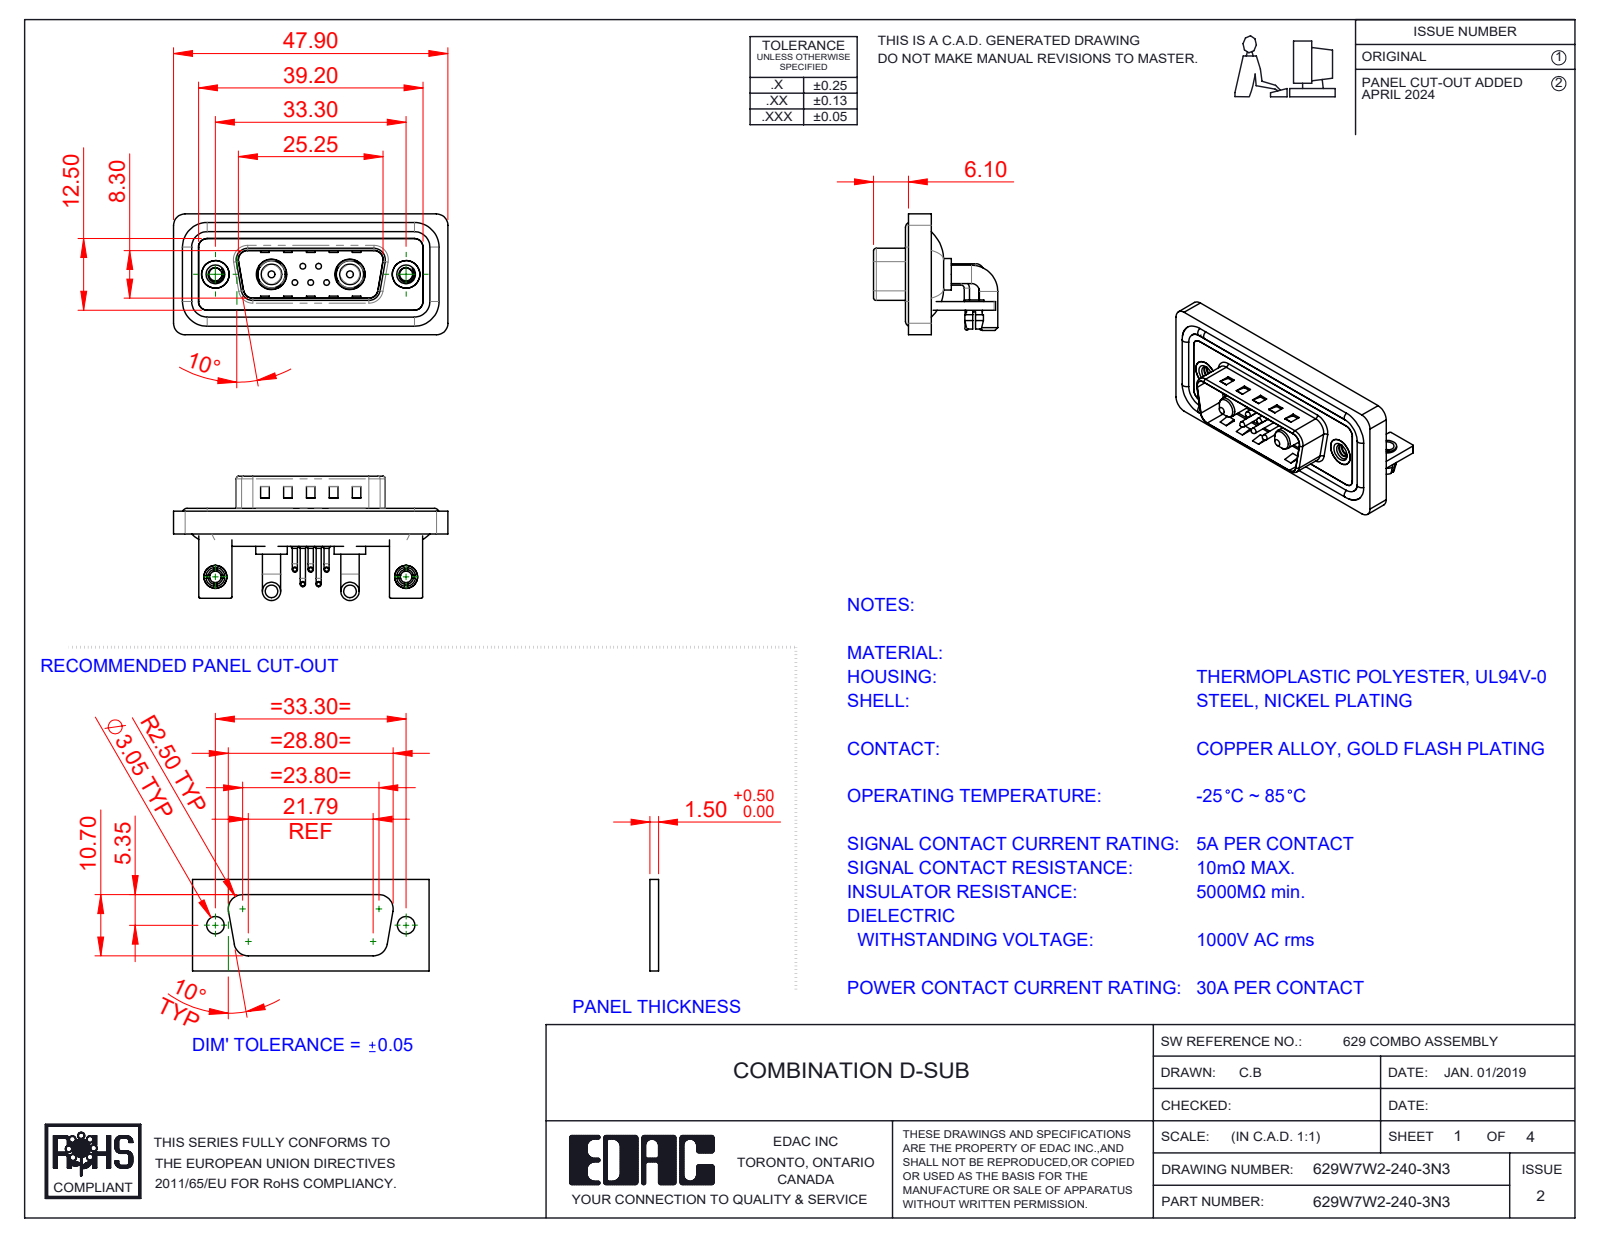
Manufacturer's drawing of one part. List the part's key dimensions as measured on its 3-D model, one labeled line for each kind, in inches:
Part name (STEP PRODUCT): 629Combo Threaded Rivet_3; 629Combo Waterproof Housing_15 Contacts; 629Combo Contact Row 2; Power Pin_30A RA (+7 more)
STEP written by: SolidWorks 2023 (CONFIG_CONTROL_DESIGN)
Units: inches
Bodies: 20 solids, 1215 faces (585 planar, 456 cylindrical, 174 other)
Overall size (bounding box): 1.886 × 0.854 × 0.831
Volume: 0.369 in³ · Surface area: 15.46 in²
Round holes (diameter × count): ⌀0.079 ×7, ⌀0.03 ×5, ⌀0.063 ×5, ⌀0.089 ×2, ⌀0.098 ×2, ⌀0.126 ×2, ⌀0.157 ×2, ⌀0.189 ×2, ⌀0.191 ×2, ⌀0.197 ×2, ⌀0.209 ×2
Round bosses / shafts (diameter × count): ⌀0.035 ×10, ⌀0.059 ×5, ⌀0.039 ×5, ⌀0.026 ×5, ⌀0.126 ×4, ⌀0.063 ×4, ⌀0.217 ×2, ⌀0.205 ×2
Partial cylindrical surfaces — rounded edges, fillets, slot ends (radius × count): R0.079 ×21, R0.059 ×18, R0.01 ×16, R0.02 ×9, R0.063 ×8, R0.04 ×5, R0.024 ×4, R0.026 ×4
Main face-to-face distances: 0.016, 0.059, 0.031, 0.114, 0.083, 0.043, 0.063, 0.047, 0.146, 0.177
Hole centre spacings: 0.124, 0.109, 0.386, 0.925, 1.311, 0.17, 0.17, 0.198
